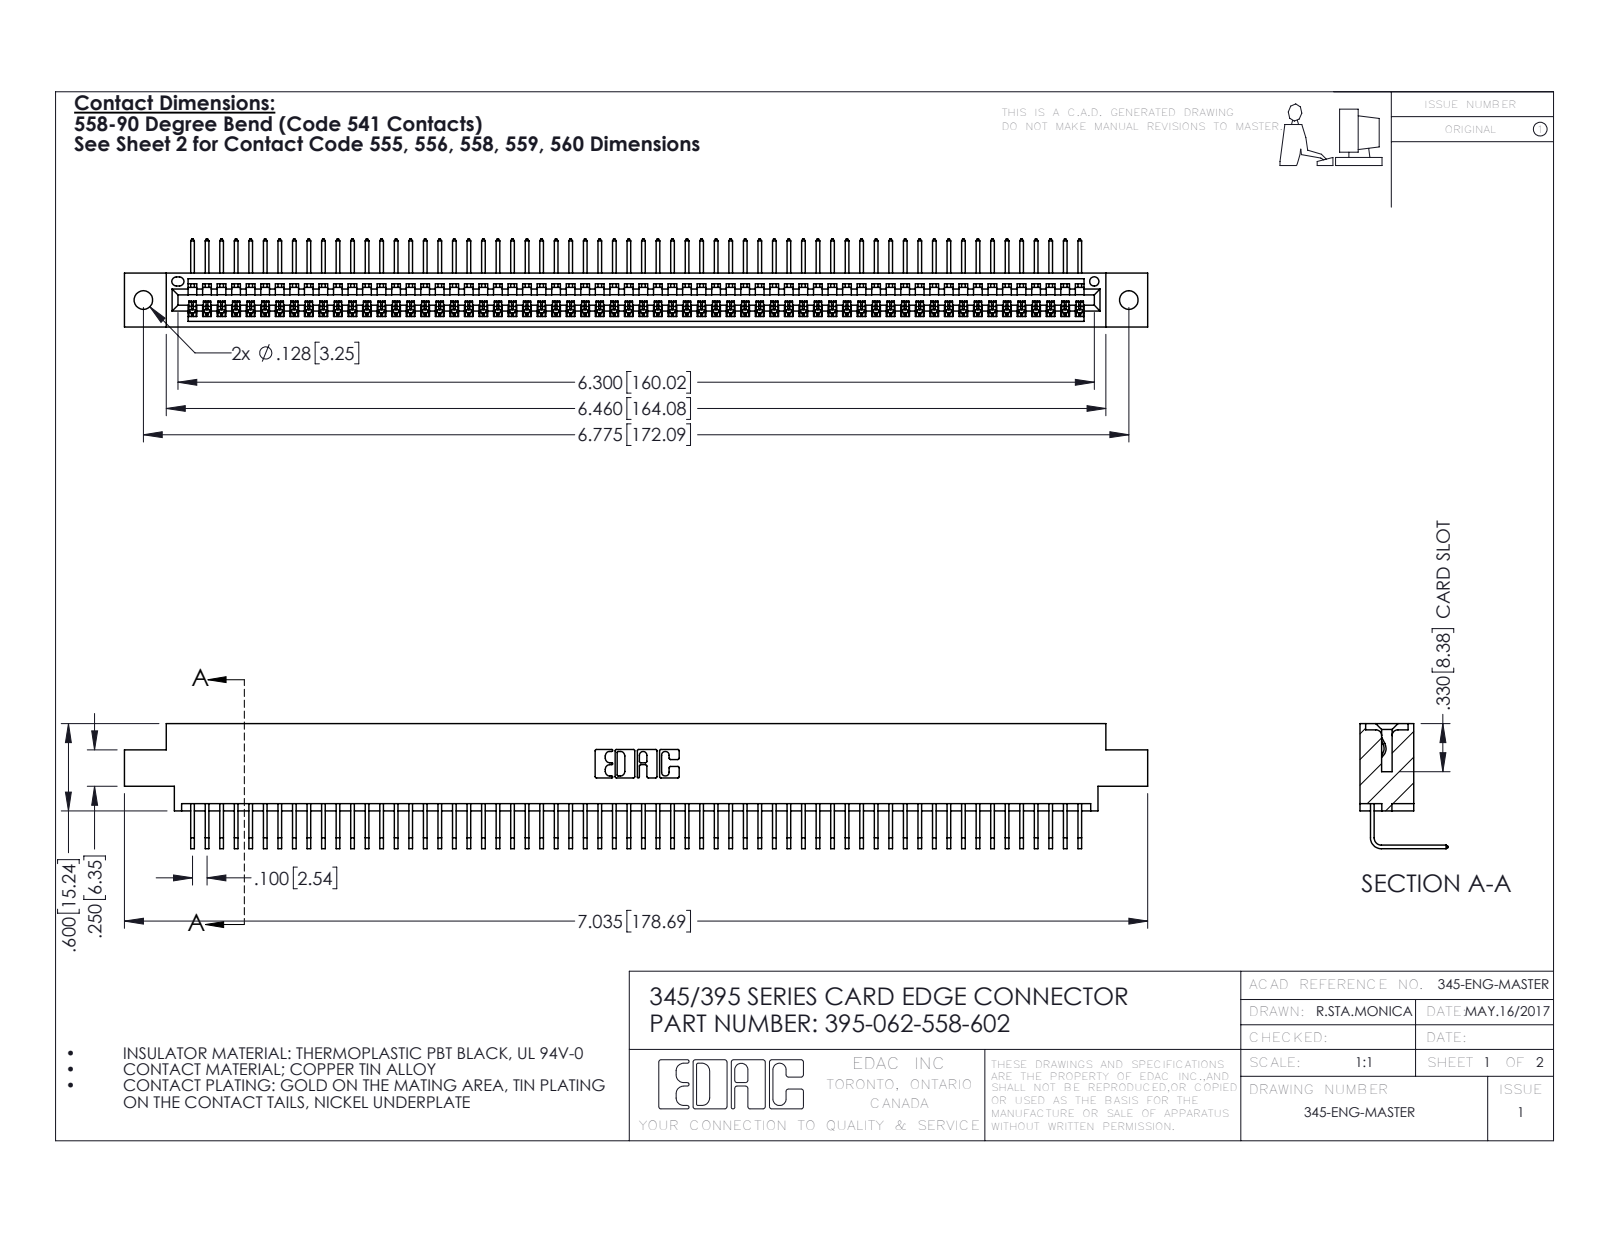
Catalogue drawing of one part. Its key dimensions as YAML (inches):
part_name: "345 Part_0.170 Offset - 0.128 Dia; 395-062-558-602; 345-292-001_558 Tail - 2"
step_written_by: "SolidWorks 2016 (CONFIG_CONTROL_DESIGN)"
units: inches
bodies: {solids: 63, faces: 3850, planar: 2688, cylindrical: 1162, other: 0}
overall_size: [7.035, 0.859, 0.605]
volume: 1.049
surface_area: 37.49
round_holes:
  - {diameter: 0.128, count: 2}
  - {diameter: 0.064, count: 1}
partial_cylinders:
  - {radius: 0.006, count: 124}
  - {radius: 0.01, count: 22}
  - {radius: 0.007, count: 6}
  - {radius: 0.031, count: 6}
  - {radius: 0.026, count: 3}
  - {radius: 0.031, count: 2}
  - {radius: 0.04, count: 2}
  - {radius: 0.014, count: 1}
face_to_face_distances: [0.072, 0.298, 0.37, 0.2, 0.098, 0.272, 0.025, 0.225, 0.175, 0.149]
hole_center_spacings: [0.27, 6.539, 6.775]
